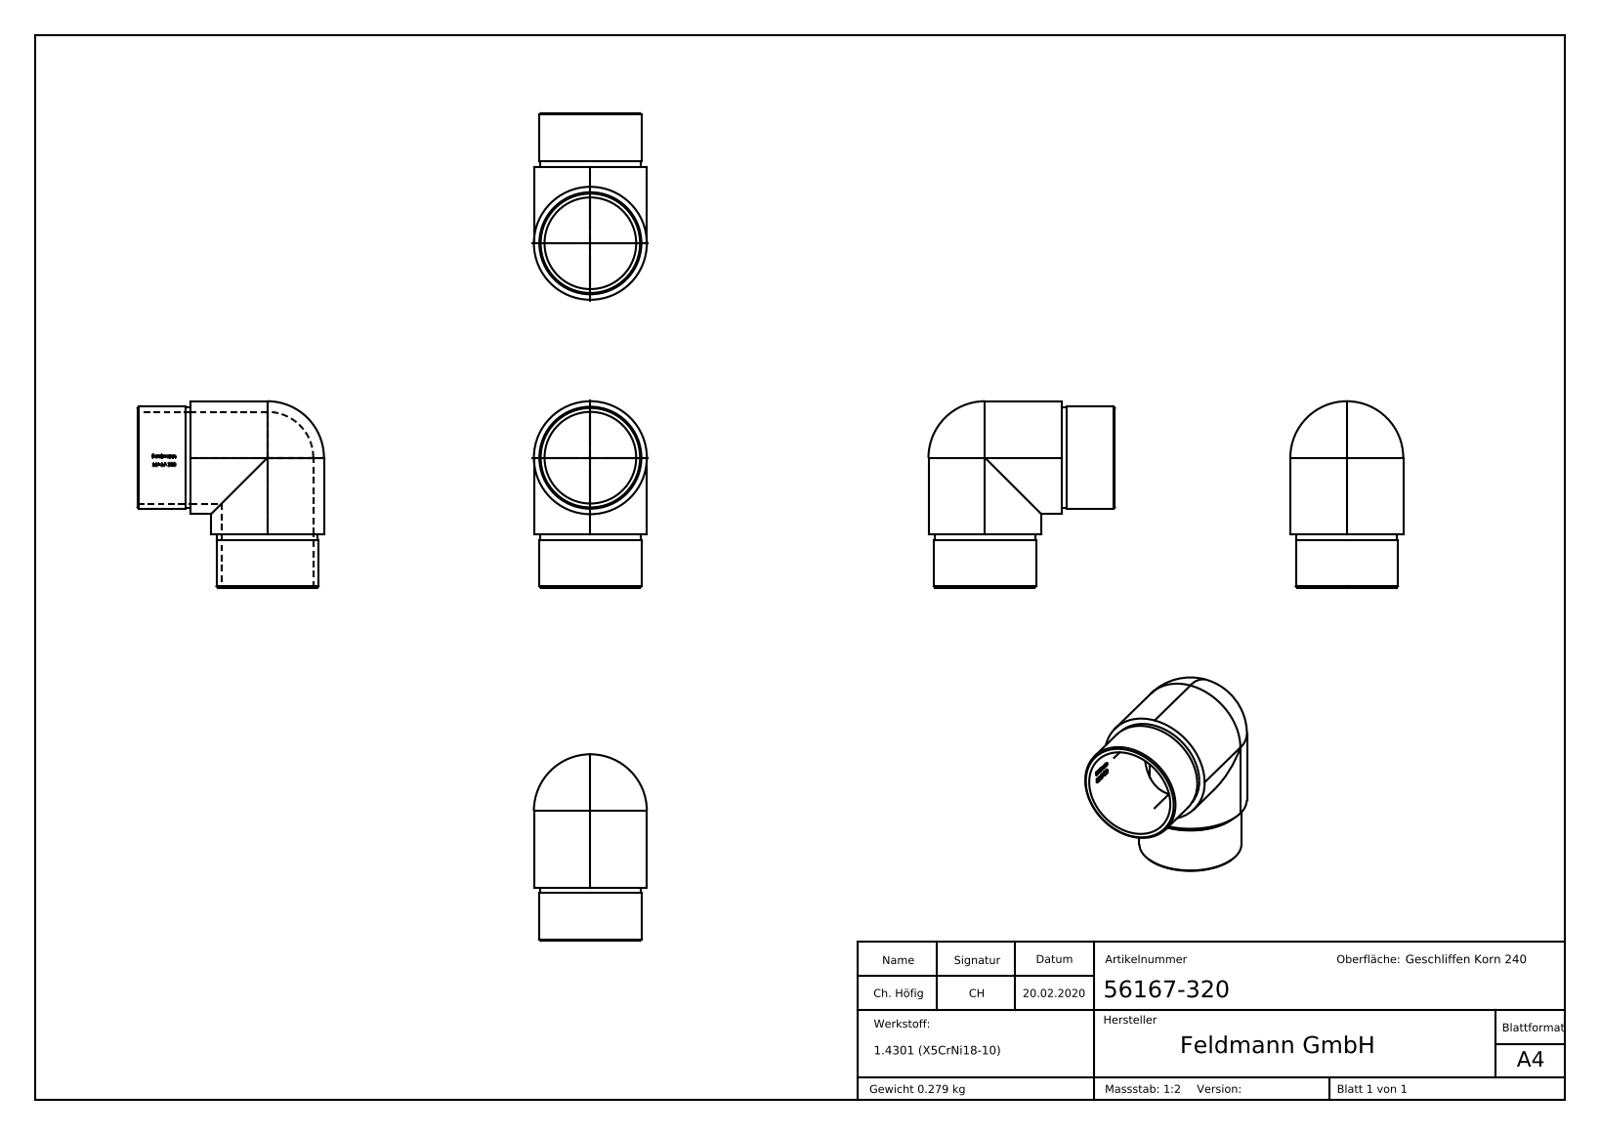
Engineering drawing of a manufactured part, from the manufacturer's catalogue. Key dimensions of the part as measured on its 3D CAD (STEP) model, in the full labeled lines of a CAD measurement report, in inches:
Part name (STEP PRODUCT): 56167-320
STEP written by: SolidWorks 2015 (CONFIG_CONTROL_DESIGN)
Units: inches
Bodies: 1 solid, 250 faces (94 planar, 38 cylindrical, 118 other)
Overall size (bounding box): 2.756 × 2.756 × 1.669
Volume: 2.154 in³ · Surface area: 36.31 in²
Round holes (diameter × count): ⌀1.354 ×2
Round bosses / shafts (diameter × count): ⌀1.669 ×2, ⌀1.508 ×2, ⌀1.492 ×2
Partial cylindrical surfaces — rounded edges, fillets, slot ends (radius × count): R0.697 ×1
Main face-to-face distances: 0.787, 0.709, 0.079, 0.015, 0.05, 0.117, 0.167, 0.052, 0.144, 0.129
